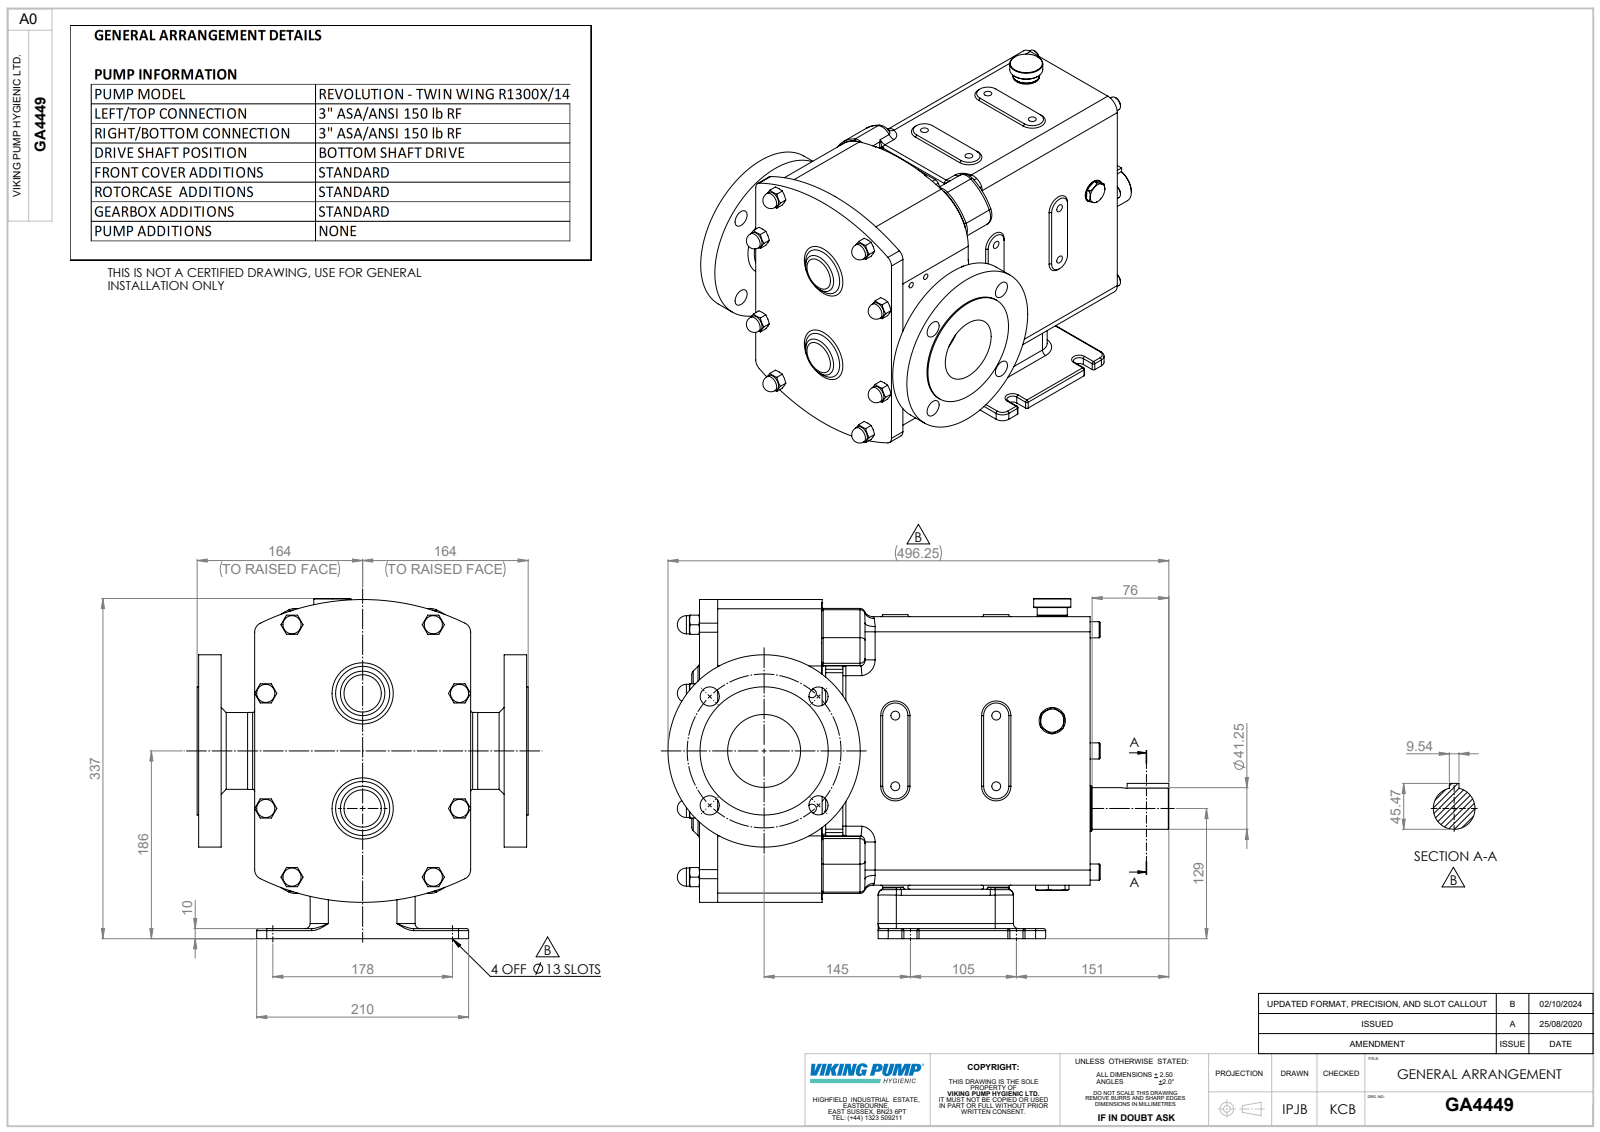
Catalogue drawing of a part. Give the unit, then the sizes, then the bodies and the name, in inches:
Units: inches
Overall size (bounding box): 19.537 × 13.268 × 12.913
Round holes (diameter × count): ⌀0.346 ×8, ⌀0.748 ×6, ⌀0.268 ×4, ⌀0.339 ×2, ⌀1.331 ×1, ⌀2.846 ×1
Round bosses / shafts (diameter × count): ⌀0.709 ×8, ⌀0.63 ×6, ⌀7.5 ×1, ⌀5 ×1, ⌀3.004 ×1, ⌀2.996 ×1, ⌀2.008 ×1, ⌀1.772 ×1
Partial cylindrical surfaces — rounded edges, fillets, slot ends (radius × count): R0.079 ×38, R0.394 ×30, R0.197 ×19, R0.232 ×8, R0.591 ×8, R0.709 ×8, R0.118 ×4, R0.236 ×4
Main face-to-face distances: 5.984, 4.783, 2.528, 8.512, 10.453, 15.236, 2.185, 1.307, 9.732, 1.22
Hole centre spacings: 3, 2.756, 3.937, 4.243, 4.806, 6, 0.28, 0.906
Volume: 1 204 in³ · Surface area: 1 308 in²
Bodies: 3 solids, 930 faces (292 planar, 295 cylindrical, 343 other)
Part name (STEP PRODUCT): Copy of R1300 CPP H BSD^GA4449; GA4449; Copy of Z94-5301-55 - 3 INCH ASA 150^GA4449
STEP written by: SolidWorks 2023 (AUTOMOTIVE_DESIGN)
